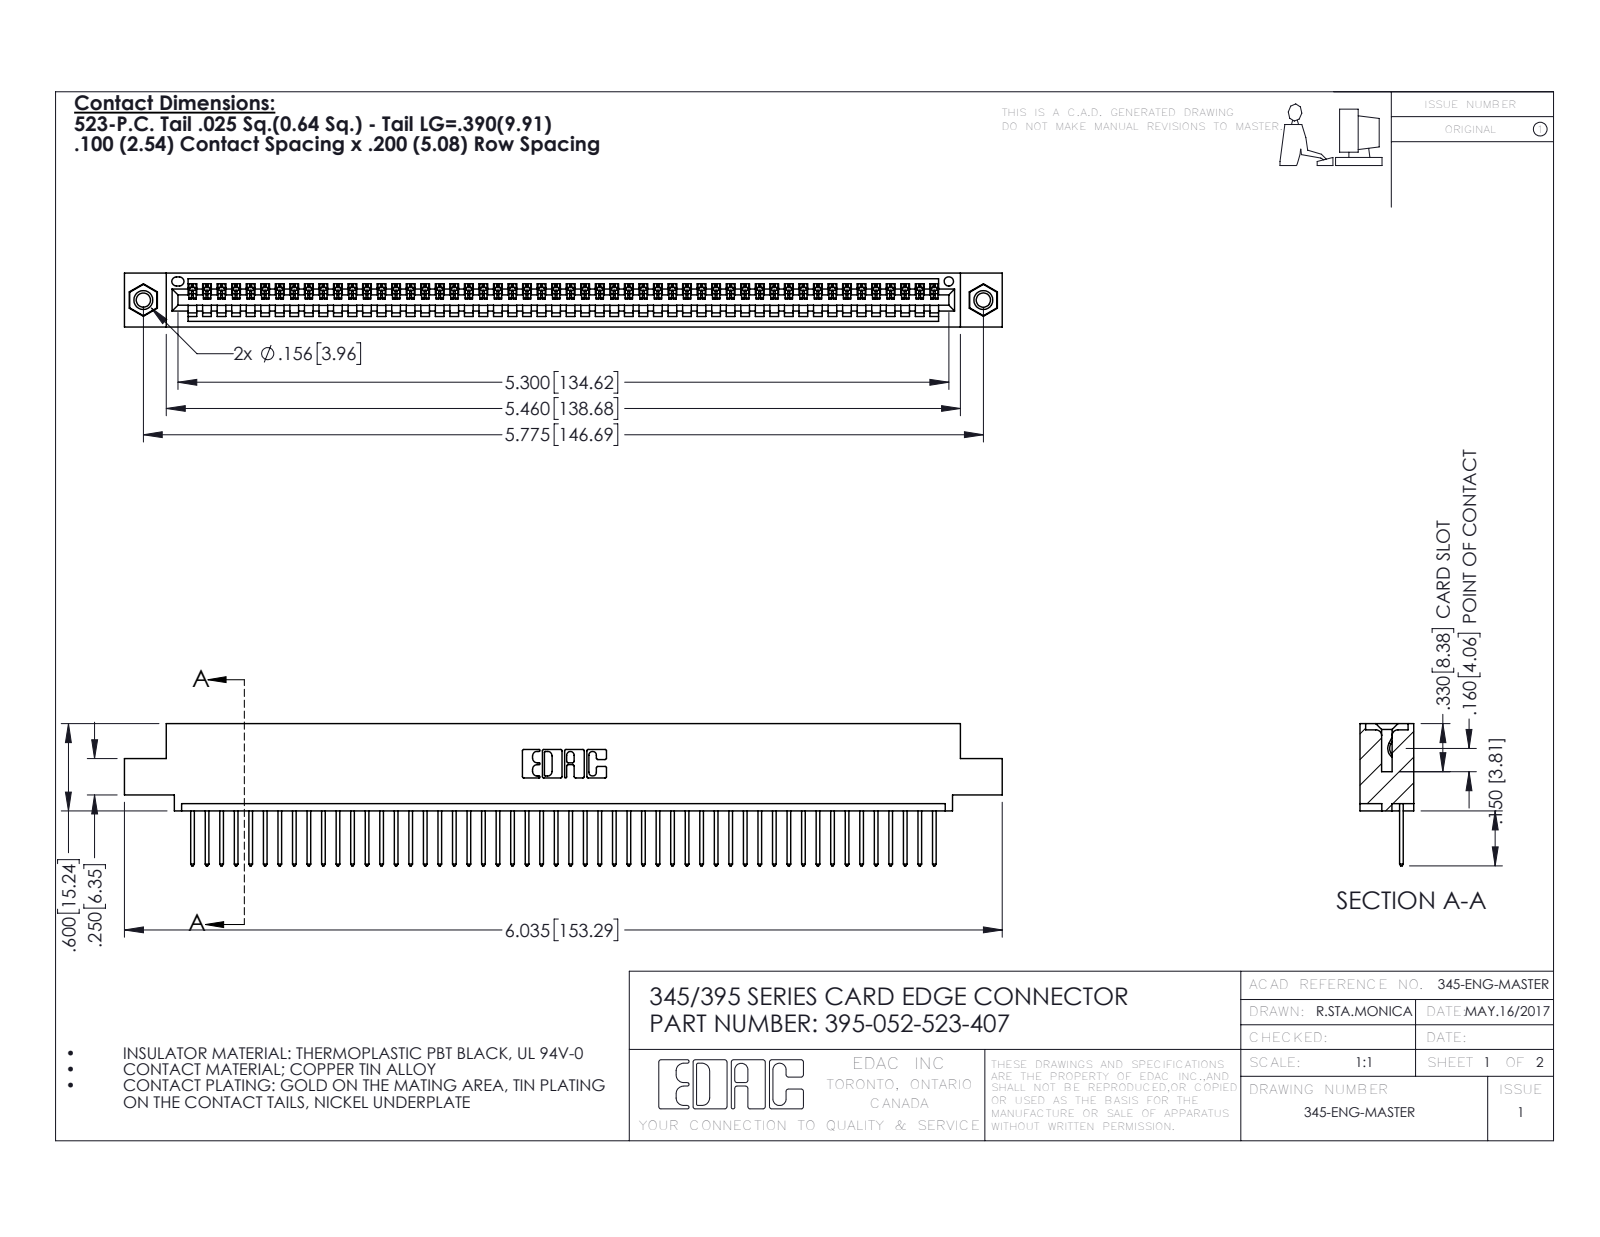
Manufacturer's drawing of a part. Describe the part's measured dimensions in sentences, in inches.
The part is named "395-052-523-407; 345-250-001_345-250-005-103; 345 Part_0.110 Offset - 0.156 Dia-TI; 345-292-001_345-293-123". Its 3-D file was written by "SolidWorks 2016 (CONFIG_CONTROL_DESIGN)". It is 55 solids with 3206 faces: 2196 planar, 994 cylindrical and 16 other. Overall it measures 6.035 by 0.977 by 0.37 inches. Its volume is 0.887 cubic inches and its surface area 30.41 square inches. Round holes: 2 of diameter 0.098, 2 of diameter 0.125, 2 of diameter 0.156, 1 of diameter 0.064. Round bosses or shafts: 2 of diameter 0.155. Partial cylindrical surfaces (rounded edges, fillets, slot ends): 104 of radius 0.006, 104 of radius 0.01, 22 of radius 0.01, 6 of radius 0.007, 6 of radius 0.031, 3 of radius 0.026, 2 of radius 0.031, 2 of radius 0.04. The main face-to-face distances are 0.072, 0.298, 0.37, 0.2, 0.098, 0.272, 0.025, 0.225, 0.149, 0.072. The hole center spacings are 0.27, 5.539, 5.775.
